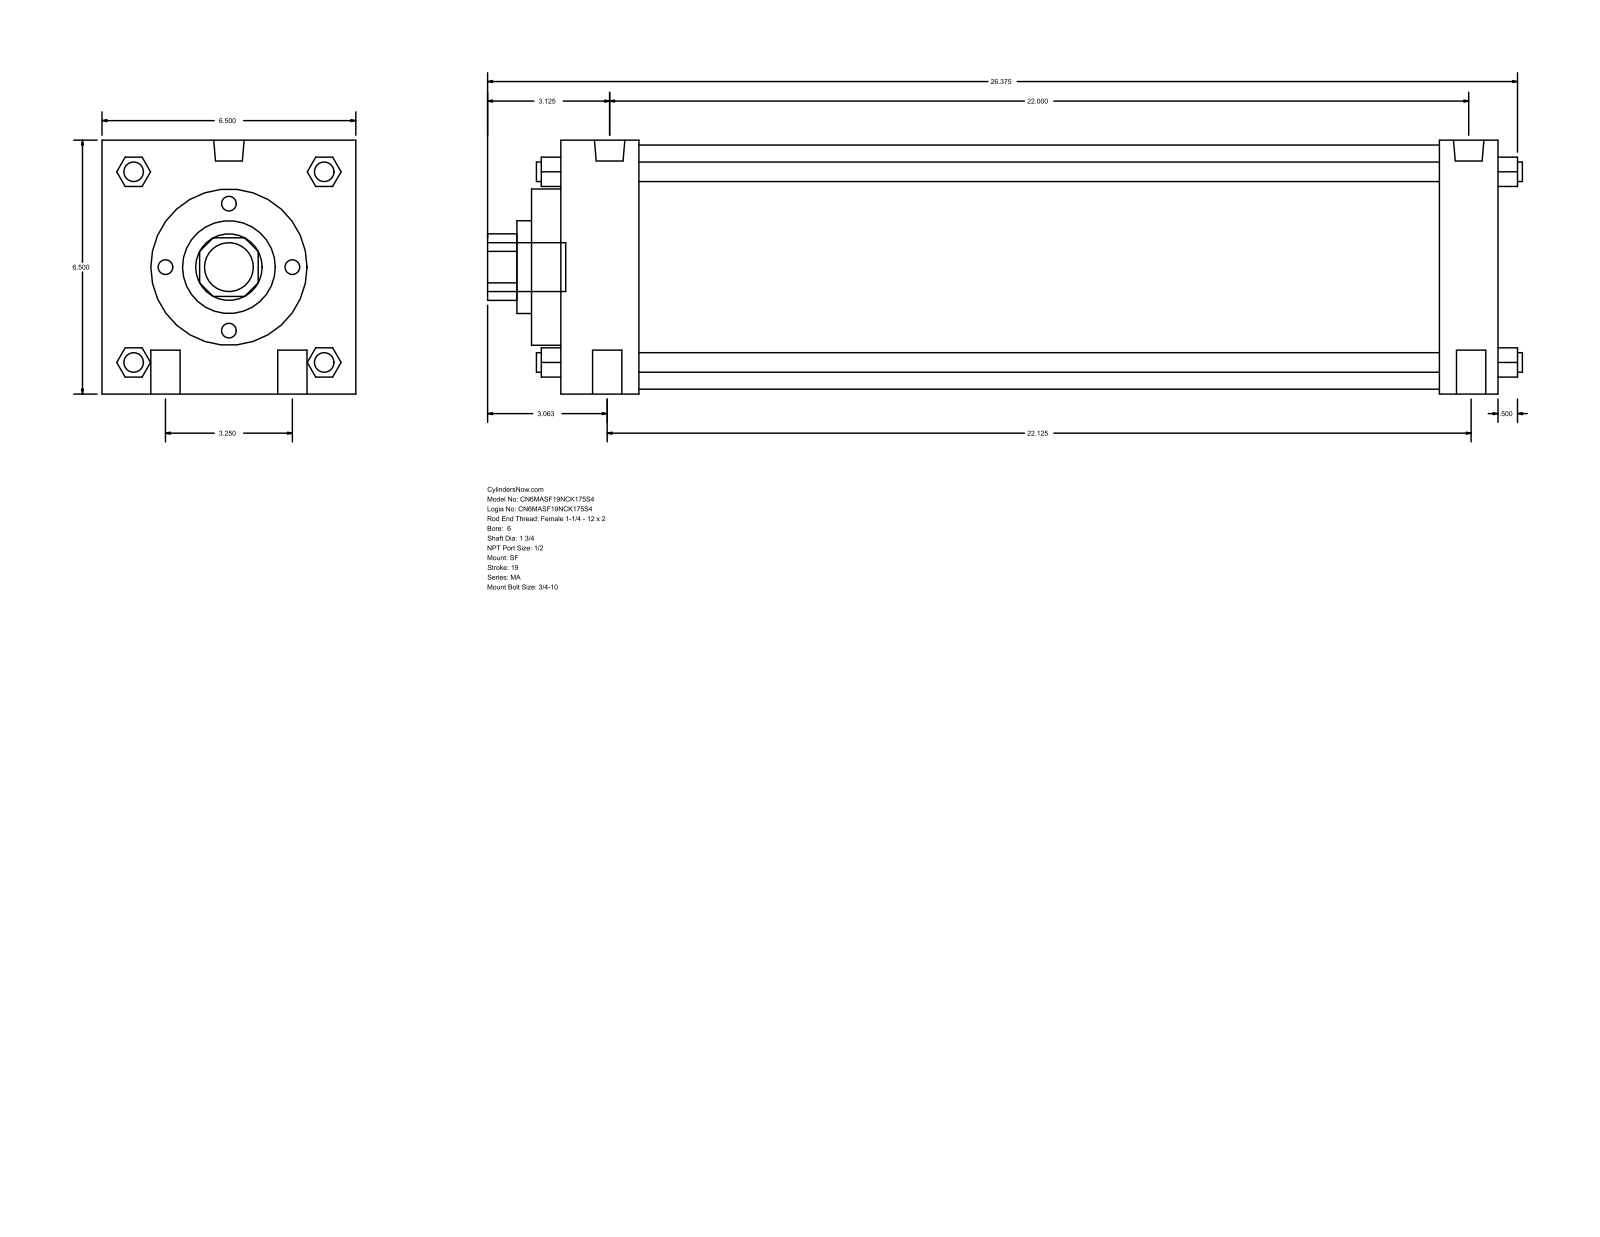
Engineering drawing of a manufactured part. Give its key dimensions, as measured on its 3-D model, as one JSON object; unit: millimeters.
{"part_name": "MA_SF__0600_1.75", "step_written_by": "GSSL Pune (CONFIG_CONTROL_DESIGN)", "units": "millimeters", "bodies": {"solids": 0, "faces": 126, "planar": 95, "cylindrical": 31, "other": 0}, "overall_size": [673.1, 165.1, 165.1], "round_holes": [[44.45, 1], [60.33, 1], [101.6, 1], [158.75, 1]], "round_bosses_or_shafts": [[19.05, 4], [12.7, 4], [19.77, 2], [17.46, 2], [31.75, 1]], "partial_cylinders_radius": [[21.63, 1]], "face_to_face_distances": [165.1, 609.61, 19.05, 50.8, 571.5, 38.11, 520.7, 558.81, 69.85, 590.55]}
